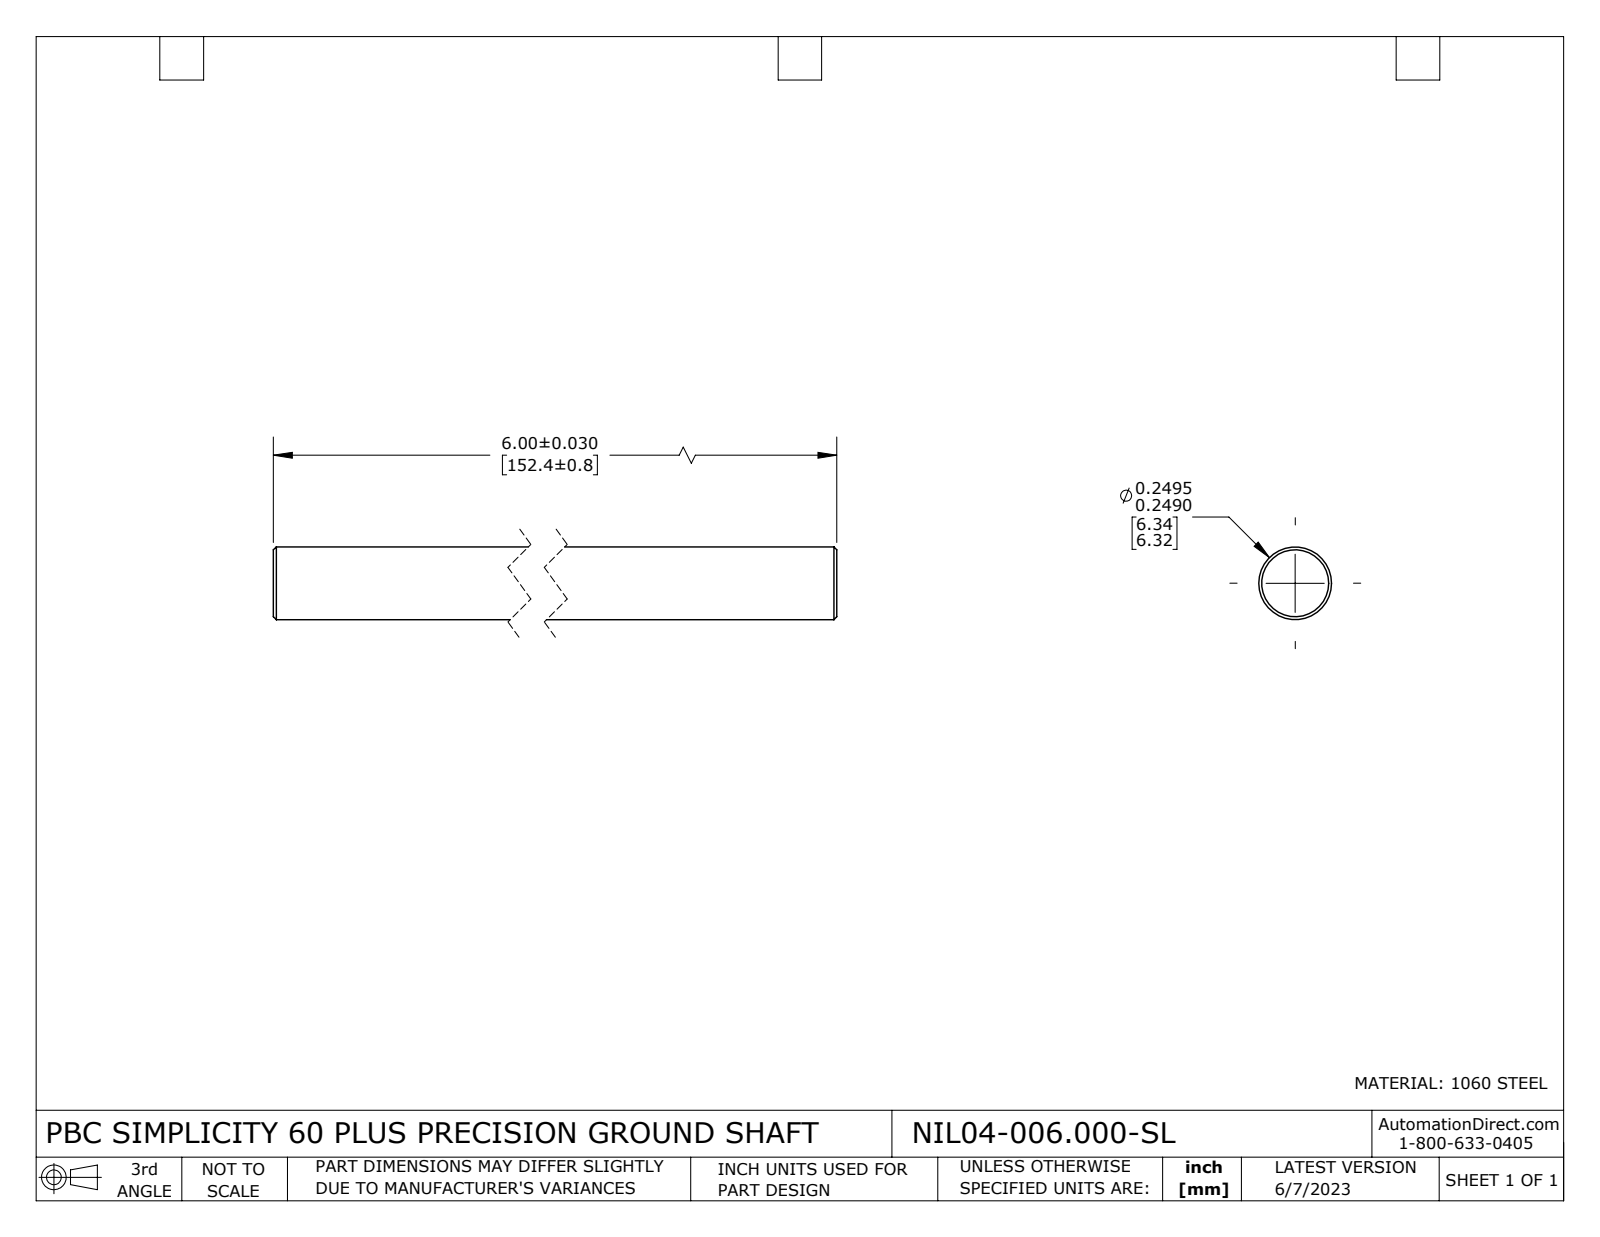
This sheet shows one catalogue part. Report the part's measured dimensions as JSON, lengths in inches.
{"part_name": "NIL04-006.000-SL", "step_written_by": "SolidWorks 2021 (CONFIG_CONTROL_DESIGN)", "units": "inches", "bodies": {"solids": 1, "faces": 8, "planar": 2, "cylindrical": 2, "other": 4}, "overall_size": [6, 0.25, 0.25], "volume_in3": 0.294, "surface_area_in2": 4.801, "round_bosses_or_shafts": [[0.25, 1]], "face_to_face_distances": [6]}
